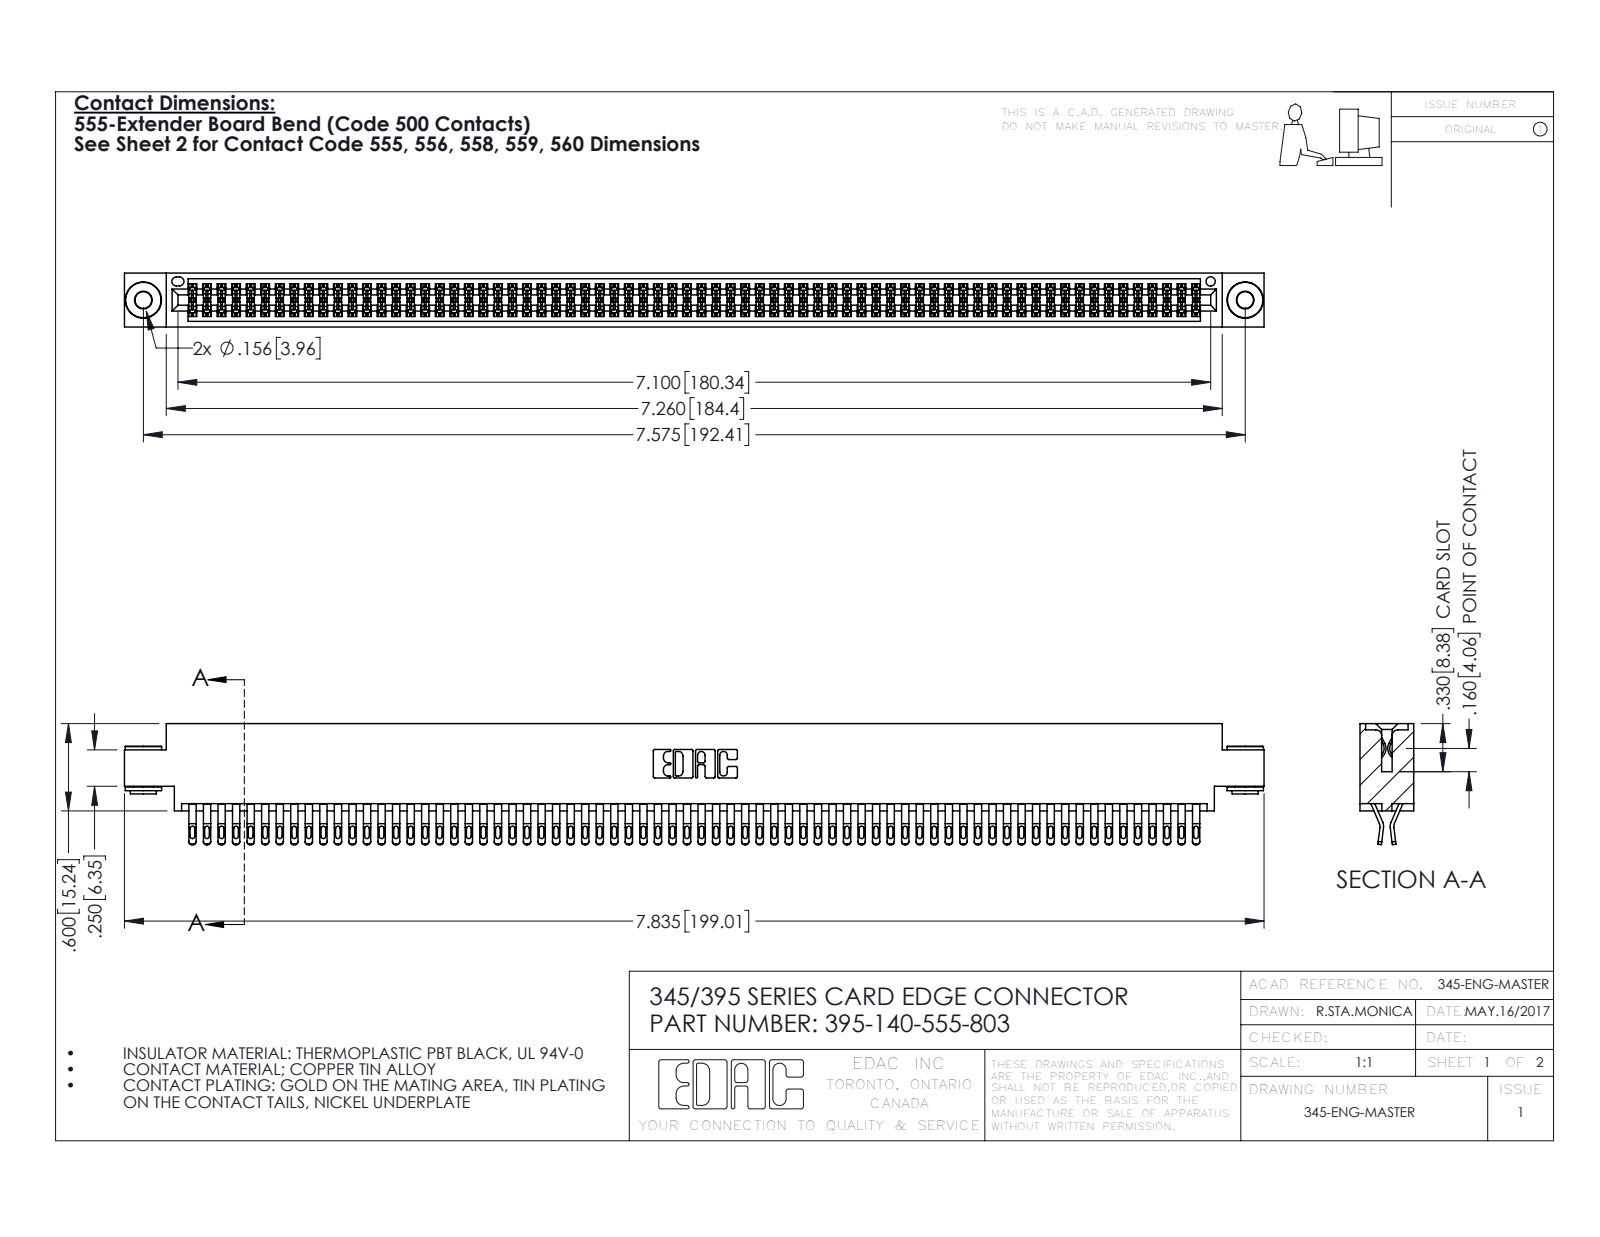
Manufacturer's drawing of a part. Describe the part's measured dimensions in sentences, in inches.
The part is named "395-140-555-803; 345-250-002_345-250-002-102; 345-292-001_555 Tail; 345 Part_0.170 Offset - 0.156 Dia-TH". Its 3-D file was written by "SolidWorks 2016 (CONFIG_CONTROL_DESIGN)". It is 143 solids with 8008 faces: 4434 planar, 3566 cylindrical and 8 other. Overall it measures 7.835 by 0.832 by 0.37 inches. Its volume is 1.215 cubic inches and its surface area 49.17 square inches. Round holes: 2 of diameter 0.116, 2 of diameter 0.156, 1 of diameter 0.064. Round bosses or shafts: 2 of diameter 0.25, 2 of diameter 0.18, 2 of diameter 0.136. Partial cylindrical surfaces (rounded edges, fillets, slot ends): 350 of radius 0.016, 280 of radius 0.02, 210 of radius 0.006, 22 of radius 0.01, 6 of radius 0.007, 6 of radius 0.031, 3 of radius 0.026, 2 of radius 0.01. The main face-to-face distances are 0.072, 0.298, 0.37, 0.025, 0.2, 0.098, 0.272, 0.225, 0.175, 0.149. The hole center spacings are 0.27, 7.339, 7.575.
